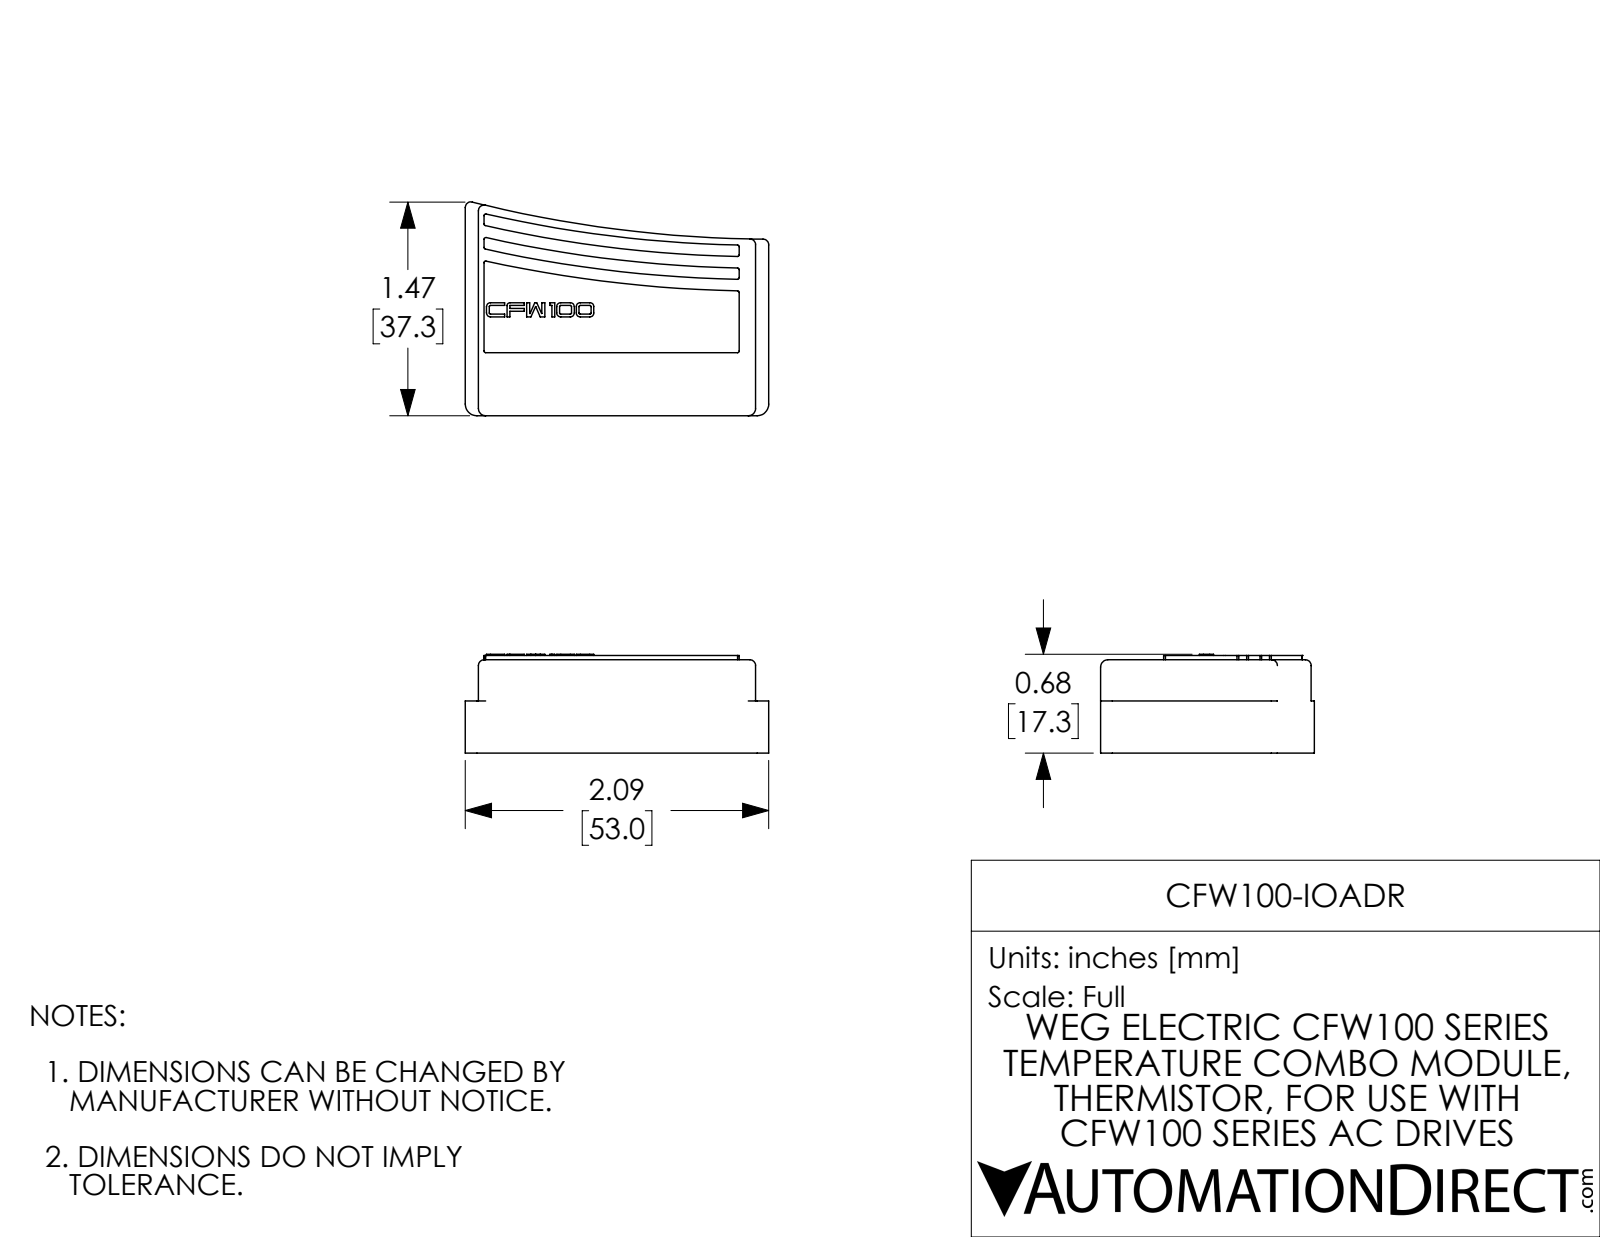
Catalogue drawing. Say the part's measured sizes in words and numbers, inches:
The part is named "IGS CFW100-IOADR". Its 3-D file was written by "SolidWorks 2017 (AUTOMOTIVE_DESIGN)". It is 1 solid with 145 faces: 83 planar, 49 cylindrical and 13 other. Overall it measures 2.087 by 1.47 by 0.68 inches. Its volume is 1.707 cubic inches and its surface area 9.948 square inches. Partial cylindrical surfaces (rounded edges, fillets, slot ends): 10 of radius 0.008, 10 of radius 0.028, 6 of radius 0.039, 3 of radius 0.05, 2 of radius 0.08, 1 of radius 0.012, 1 of radius 0.012, 1 of radius 0.012. The main face-to-face distances are 0.672, 0.642, 0.03, 0.091, 1.996, 2.087, 1.906, 0.358, 0.283, 0.313.
